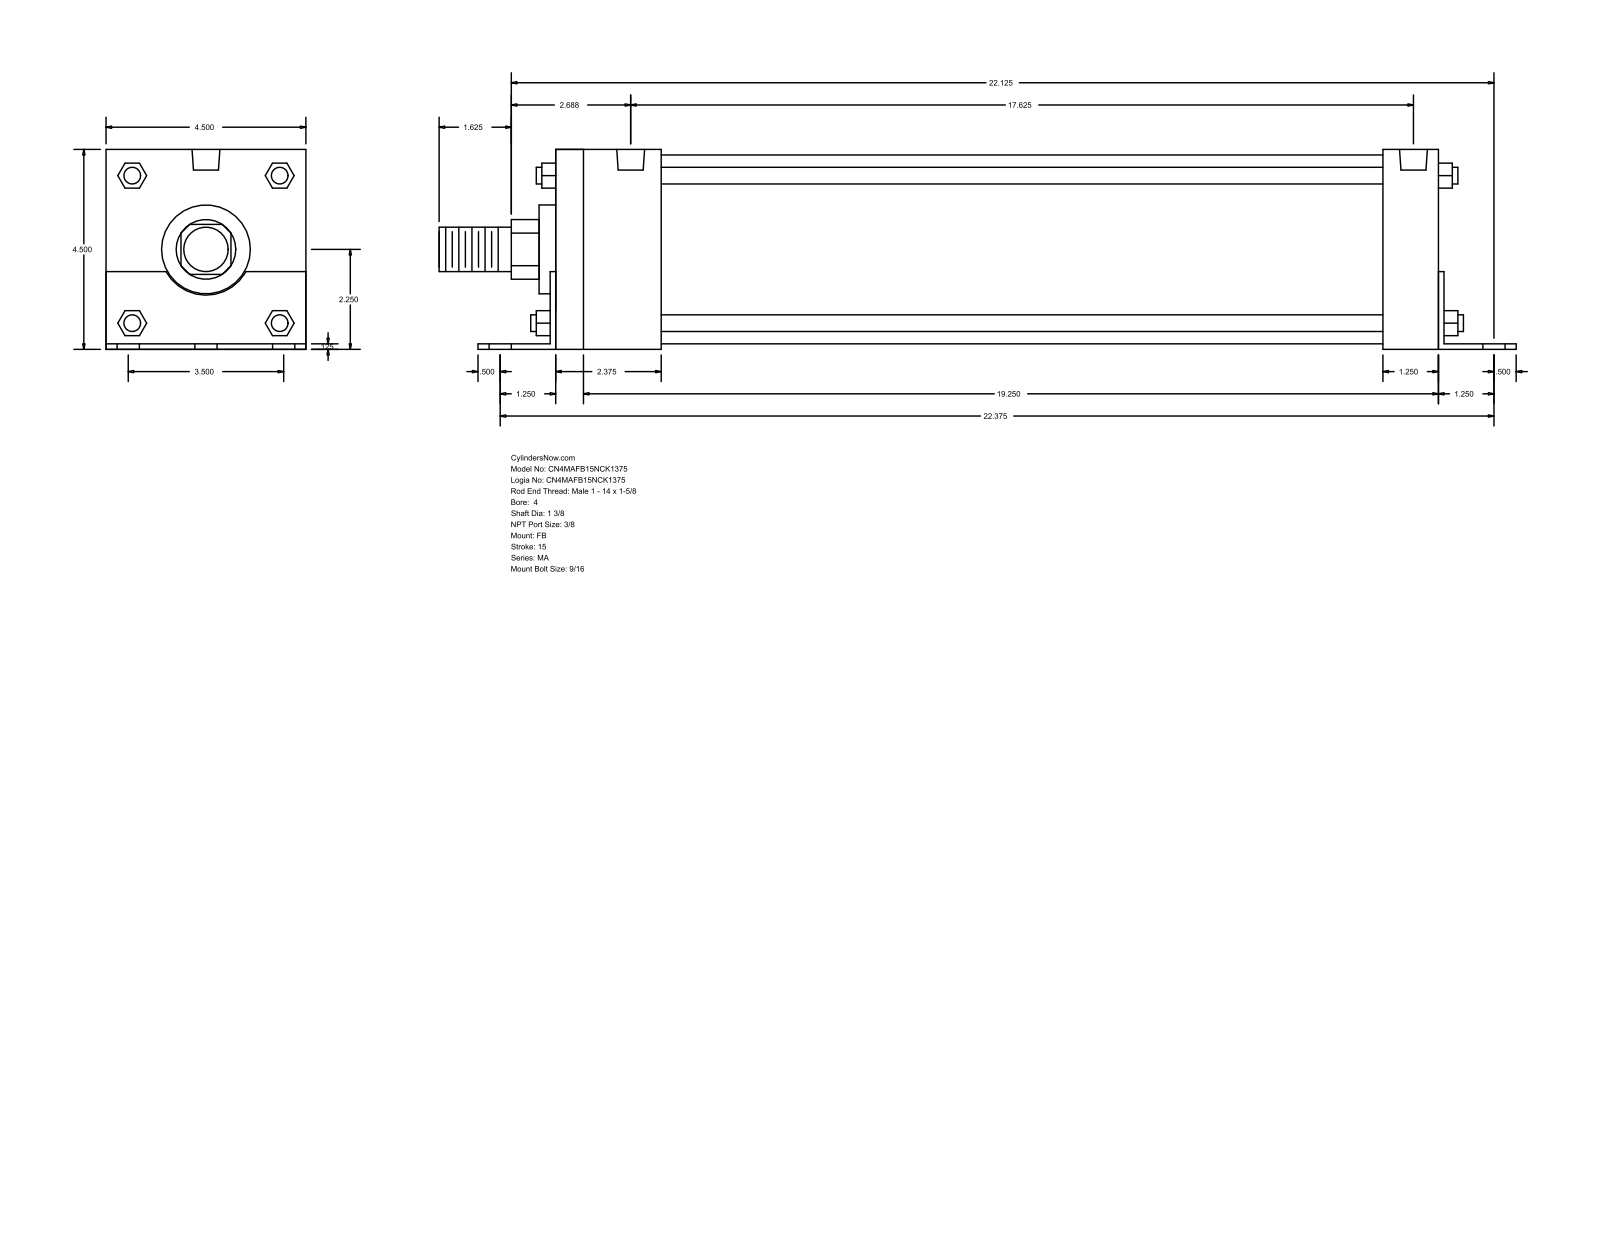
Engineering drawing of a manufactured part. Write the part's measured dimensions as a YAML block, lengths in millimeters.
part_name: "MA_FB__0400_1.375"
step_written_by: "GSSL Pune (CONFIG_CONTROL_DESIGN)"
units: millimeters
bodies: {solids: 0, faces: 140, planar: 105, cylindrical: 35, other: 0}
overall_size: [615.95, 114.35, 114.3]
round_holes:
  - {diameter: 14.29, count: 6}
  - {diameter: 11.11, count: 4}
  - {diameter: 15.93, count: 2}
round_bosses_or_shafts:
  - {diameter: 9.53, count: 4}
  - {diameter: 107.95, count: 1}
  - {diameter: 50.8, count: 1}
  - {diameter: 34.92, count: 1}
  - {diameter: 25.4, count: 1}
partial_cylinders:
  - {radius: 17.06, count: 1}
  - {radius: 26.16, count: 1}
face_to_face_distances: [114.3, 3.17, 114.35, 3.12, 111.18, 508, 504.83, 511.17, 31.75, 476.25]
hole_center_spacings: [44.45, 570.07, 568.33, 64, 67.5, 86.85, 88.9, 90.98]
